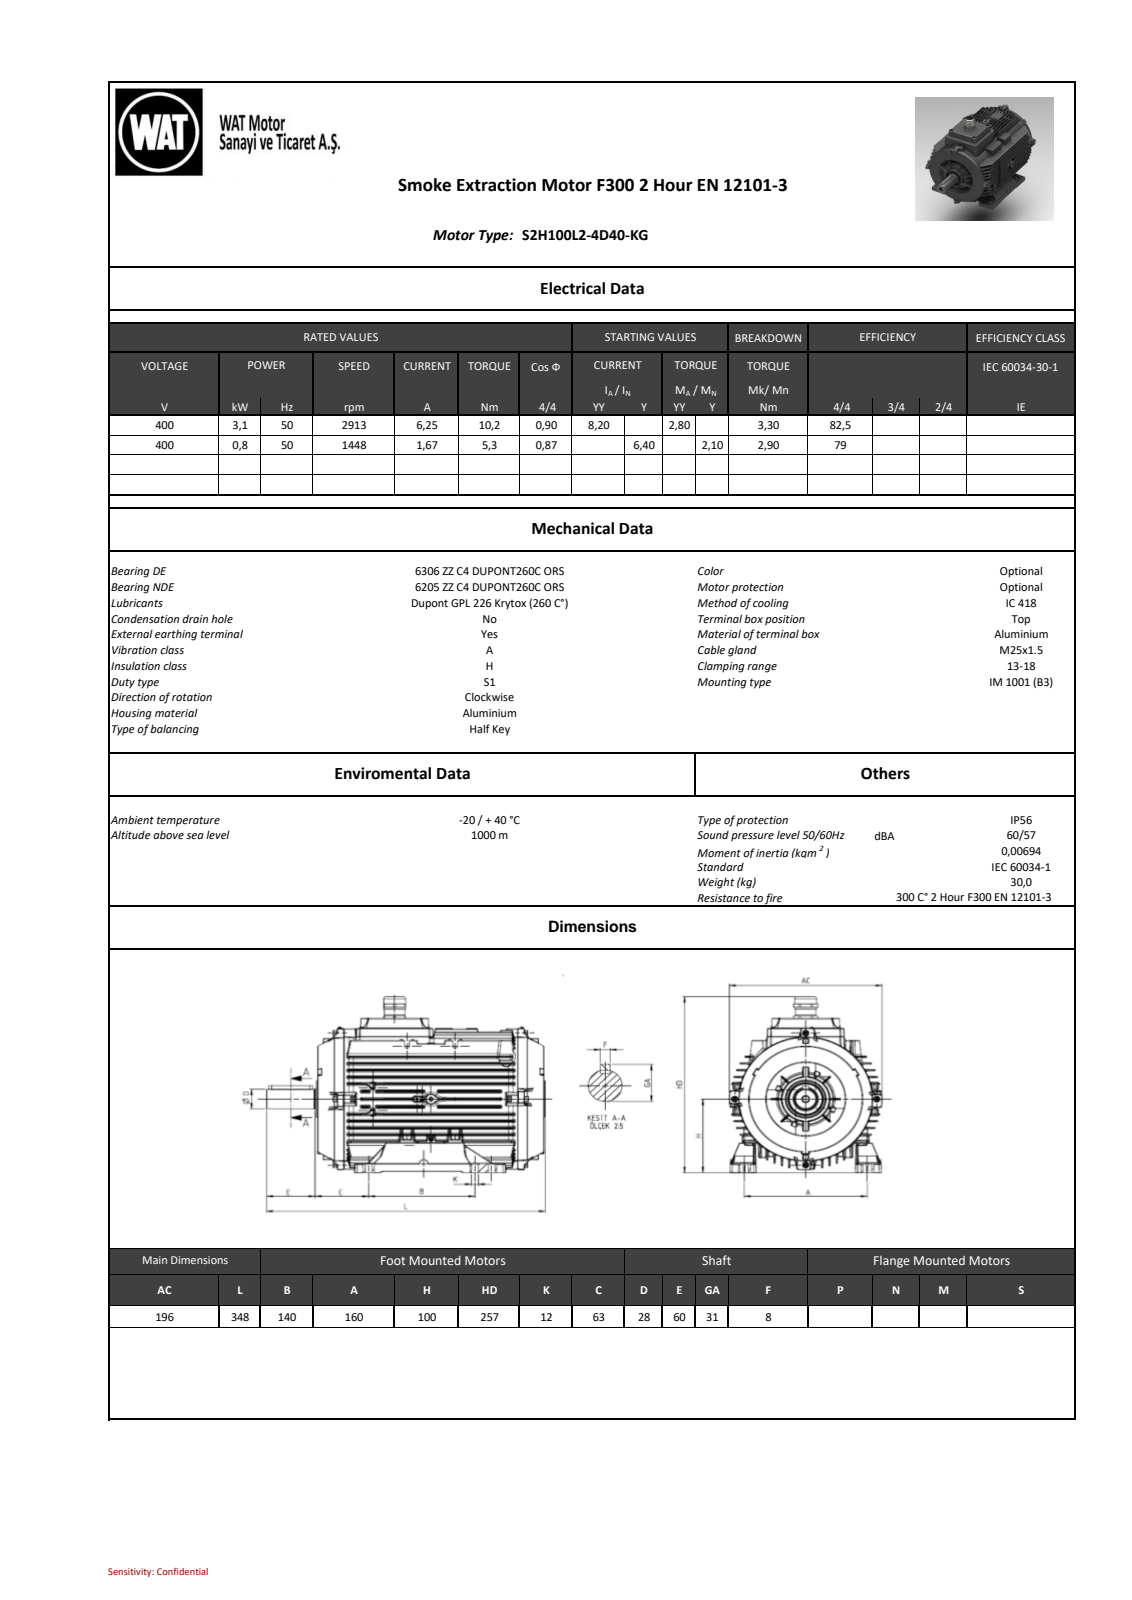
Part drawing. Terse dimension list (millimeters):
name: 26030774DB1Fe4o9
written by: SIEMENS PLM Software NX 11.0 (AUTOMOTIVE_DESIGN)
unit: mm
bodies: 0 solids, 6364 faces (1240 planar, 1855 cylindrical, 3269 other)
size: 348 × 257.2 × 196
holes: 8× ⌀6.5, 1× ⌀8.5, 1× ⌀10.5, 1× ⌀18, 1× ⌀32, 1× ⌀40, 1× ⌀43.9, 1× ⌀44.1
bosses: 4× ⌀9.2, 4× ⌀8.5, 4× ⌀8, 4× ⌀5, 1× ⌀168, 1× ⌀30, 1× ⌀29.59, 1× ⌀28.14
rounds: 619× R0.8, 301× R1, 140× R2, 94× R0.5, 85× R1.5, 59× R0.81, 16× R2.5, 16× R4.5
face distances: 8.53, 8.46, 8.45, 76.24, 16.91, 93.45, 76.68, 17.05, 25.58, 59.63
hole spacings: 10, 64, 128, 128.39, 143.11, 54, 64.56, 66.62
